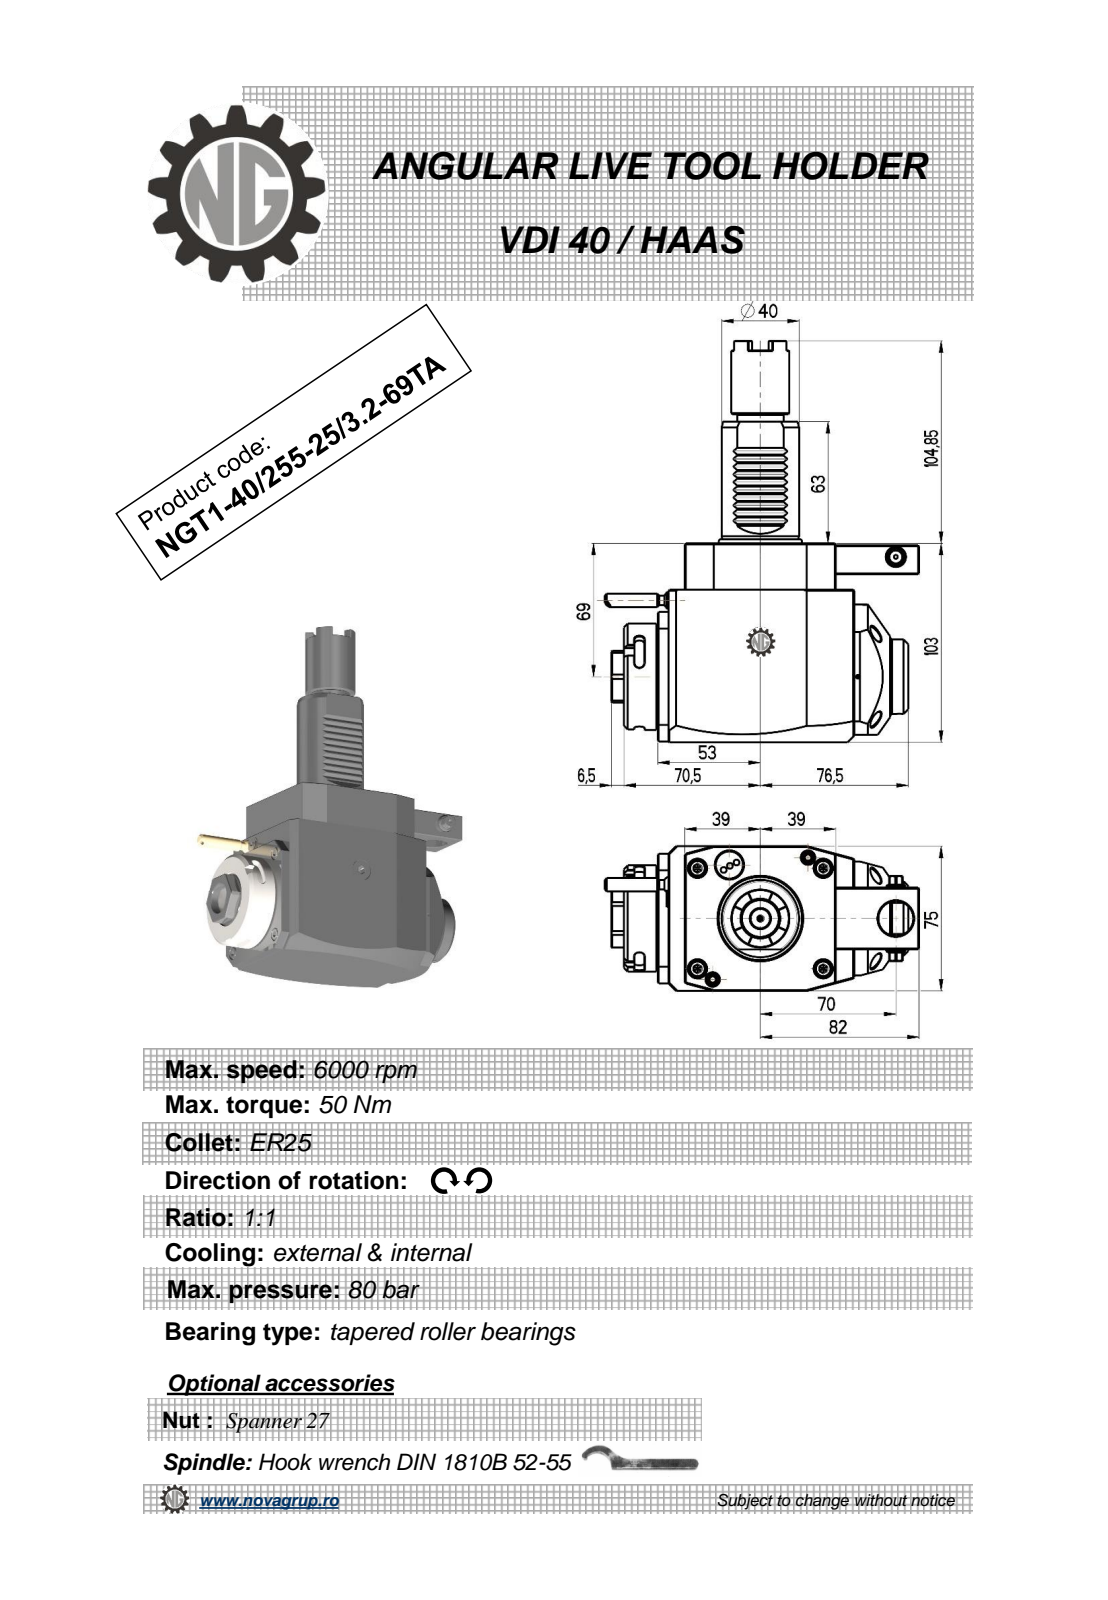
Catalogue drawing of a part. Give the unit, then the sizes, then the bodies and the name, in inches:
Units: inches
Overall size (bounding box): 8.183 × 6.391 × 2.953
Round holes (diameter × count): ⌀0.709 ×2, ⌀0.079 ×1, ⌀0.098 ×1, ⌀0.118 ×1, ⌀0.374 ×1, ⌀0.787 ×1
Round bosses / shafts (diameter × count): ⌀0.353 ×2, ⌀2.165 ×1, ⌀1.89 ×1, ⌀1.575 ×1, ⌀1.516 ×1, ⌀1.181 ×1, ⌀0.945 ×1, ⌀0.394 ×1
Partial cylindrical surfaces — rounded edges, fillets, slot ends (radius × count): R0.012 ×10, R0.098 ×6, R7.087 ×2, R0.02 ×1, R0.152 ×1, R0.167 ×1, R0.591 ×1, R0.965 ×1
Main face-to-face distances: 2.953, 4.055, 0.689, 0.906, 3.11, 4.016, 0.945, 1.24, 0.551, 3.425
Hole centre spacings: 1.107, 1.701, 2.421, 2.756
Volume: 57.2 in³ · Surface area: 115.2 in²
Bodies: 1 solid, 397 faces (213 planar, 94 cylindrical, 90 other)
Part name (STEP PRODUCT): NGT1_40_255_25_3_2_69TA
STEP written by: PRO/ENGINEER BY PARAMETRIC TECHNOLOGY CORPORATION, 2010280 (CONFIG_CONTROL_DESIGN)
